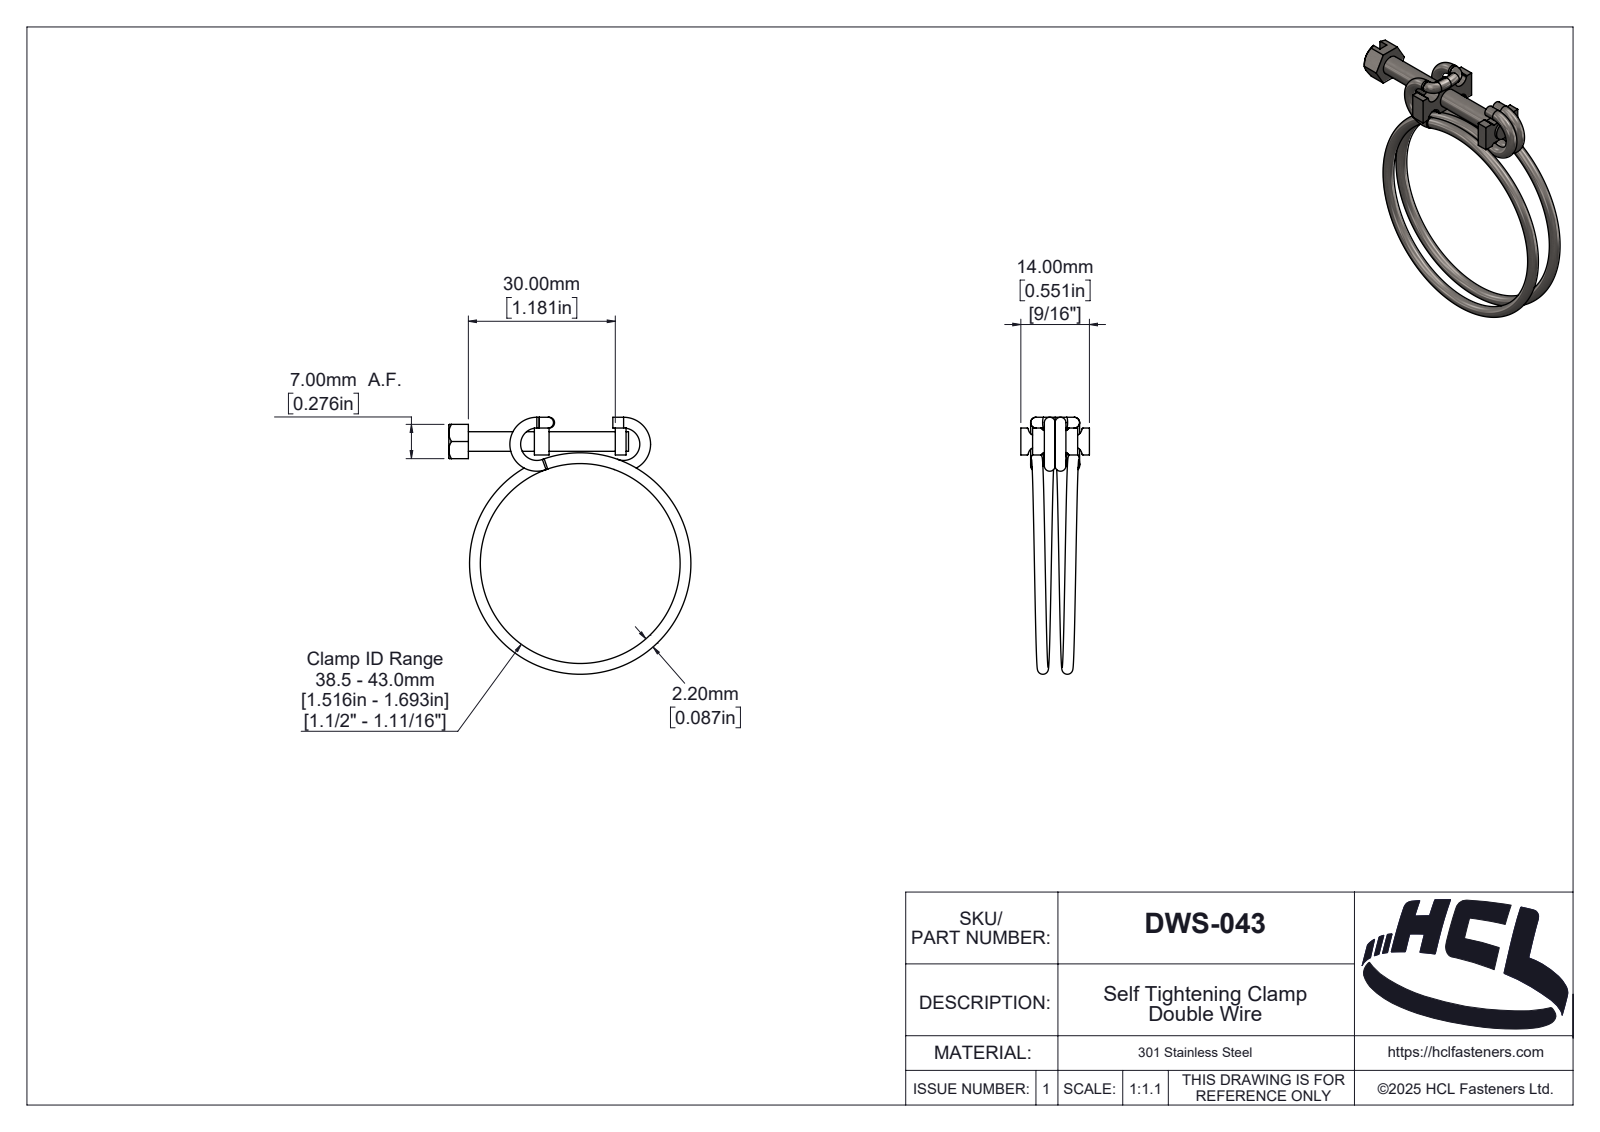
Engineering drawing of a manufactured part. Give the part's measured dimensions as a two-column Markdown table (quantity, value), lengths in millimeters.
| quantity | value |
| --- | --- |
| part name | DWS-043 |
| STEP written by | SolidWorks 2025 (AUTOMOTIVE_DESIGN) |
| units | millimeters |
| bodies | 6 solids, 209 faces (51 planar, 74 cylindrical, 84 other) |
| overall size | 52.45 × 49.44 × 14 |
| volume | 2 202 mm³ |
| surface area | 3 670 mm² |
| round holes (diameter × count) | 4 × 1 |
| round bosses / shafts (diameter × count) | 2.2 × 4 |
| partial cylindrical surfaces (radius × count) | 0.2 × 12, 0.5 × 4, 1.6 × 4, 0.4 × 1, 0.51 × 1, 0.53 × 1, 0.64 × 1, 0.91 × 1 |
| main face-to-face distances | 2, 3, 16.48, 7, 0.5, 18.72, 15.72, 16.52, 13.52, 2.2 |
